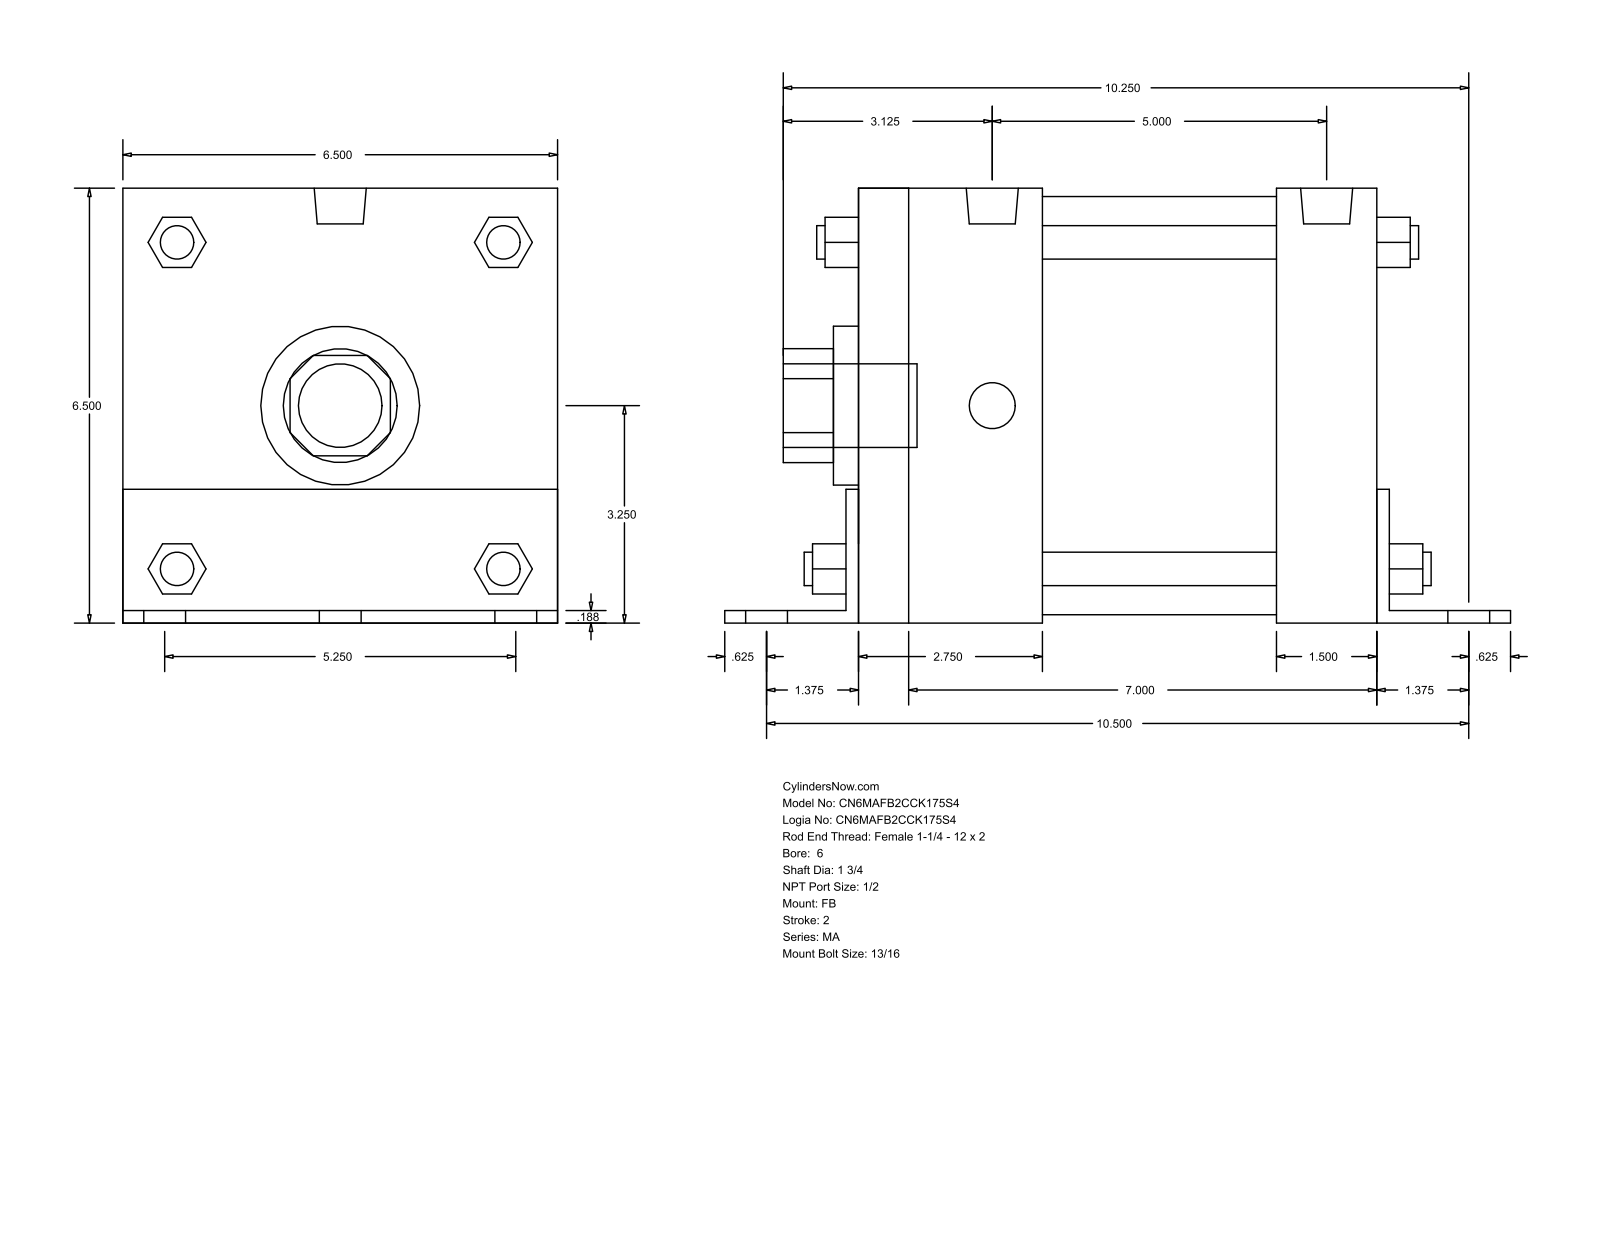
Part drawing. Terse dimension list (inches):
name: MA_FB__0600_1.75
written by: GSSL Pune (CONFIG_CONTROL_DESIGN)
unit: in
bodies: 0 solids, 140 faces (105 planar, 35 cylindrical, 0 other)
size: 11.75 × 6.502 × 6.5
holes: 1× ⌀1.75, 1× ⌀2.375, 1× ⌀6.25
bosses: 6× ⌀0.813, 4× ⌀0.687, 4× ⌀0.5, 2× ⌀0.778, 1× ⌀1.25
rounds: 1× R0.852, 1× R1.262
face distances: 6.5, 0.187, 7.75, 6.502, 7.938, 0.185, 6.315, 8.125, 1.5, 2.937
